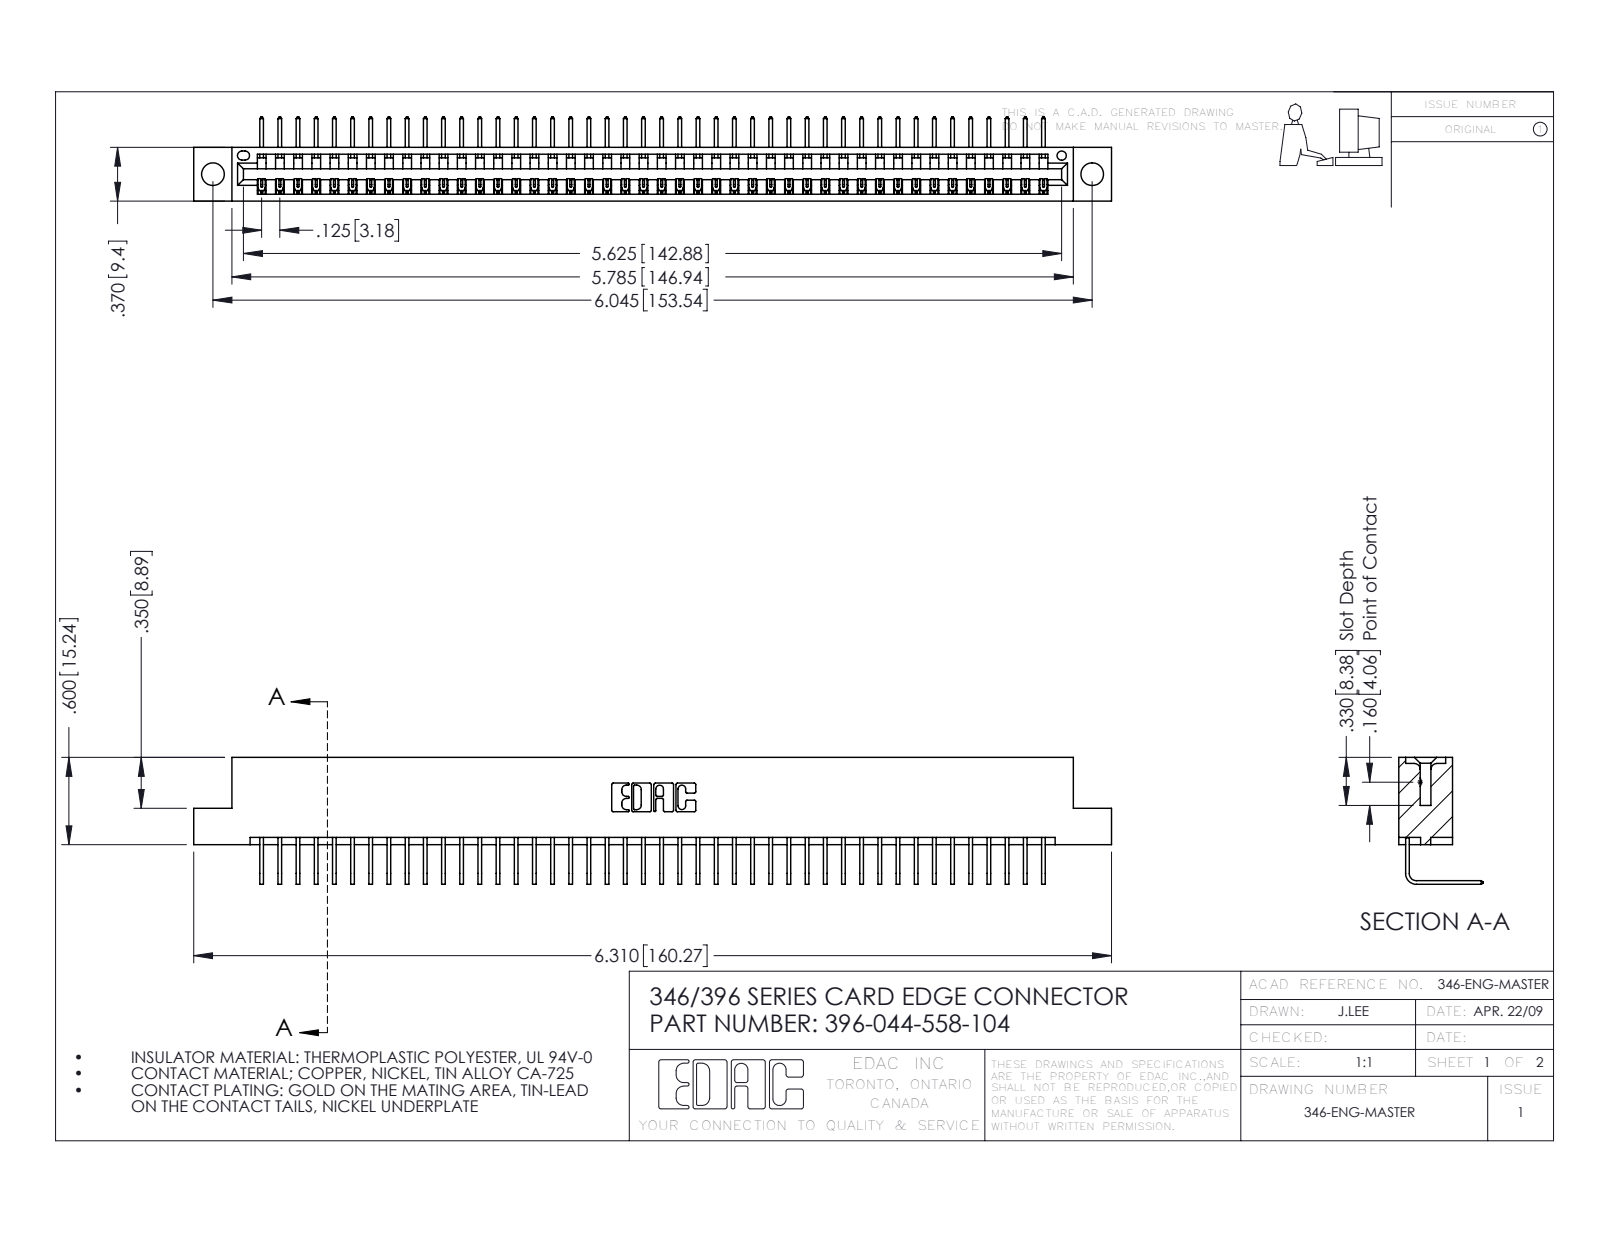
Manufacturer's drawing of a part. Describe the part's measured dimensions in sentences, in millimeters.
The part is named "396-044-558-104; 345-292-001_558 Tail - 2; 346 Part_Flush Mounting Lugs - 0.156 Dia-TH". Its 3-D file was written by "SolidWorks 2016 (CONFIG_CONTROL_DESIGN)". It is 45 solids with 2762 faces: 1924 planar, 838 cylindrical and 0 other. Overall it measures 160.3 by 22.2 by 14.7 millimeters. Its volume is 15 400 cubic millimeters and its surface area 19 970 square millimeters. Round holes: 2 of diameter 4, 1 of diameter 1.6. Partial cylindrical surfaces (rounded edges, fillets, slot ends): 88 of radius 0.2, 22 of radius 0.3, 6 of radius 0.2, 6 of radius 0.8, 3 of radius 0.7, 2 of radius 0.8, 2 of radius 1, 1 of radius 0.4. The main face-to-face distances are 8.2, 1.2, 9.4, 6.4, 7.6, 0.6, 1.8, 3.8, 5.6, 2.5. The hole center spacings are 6.2, 148.2, 153.5.
